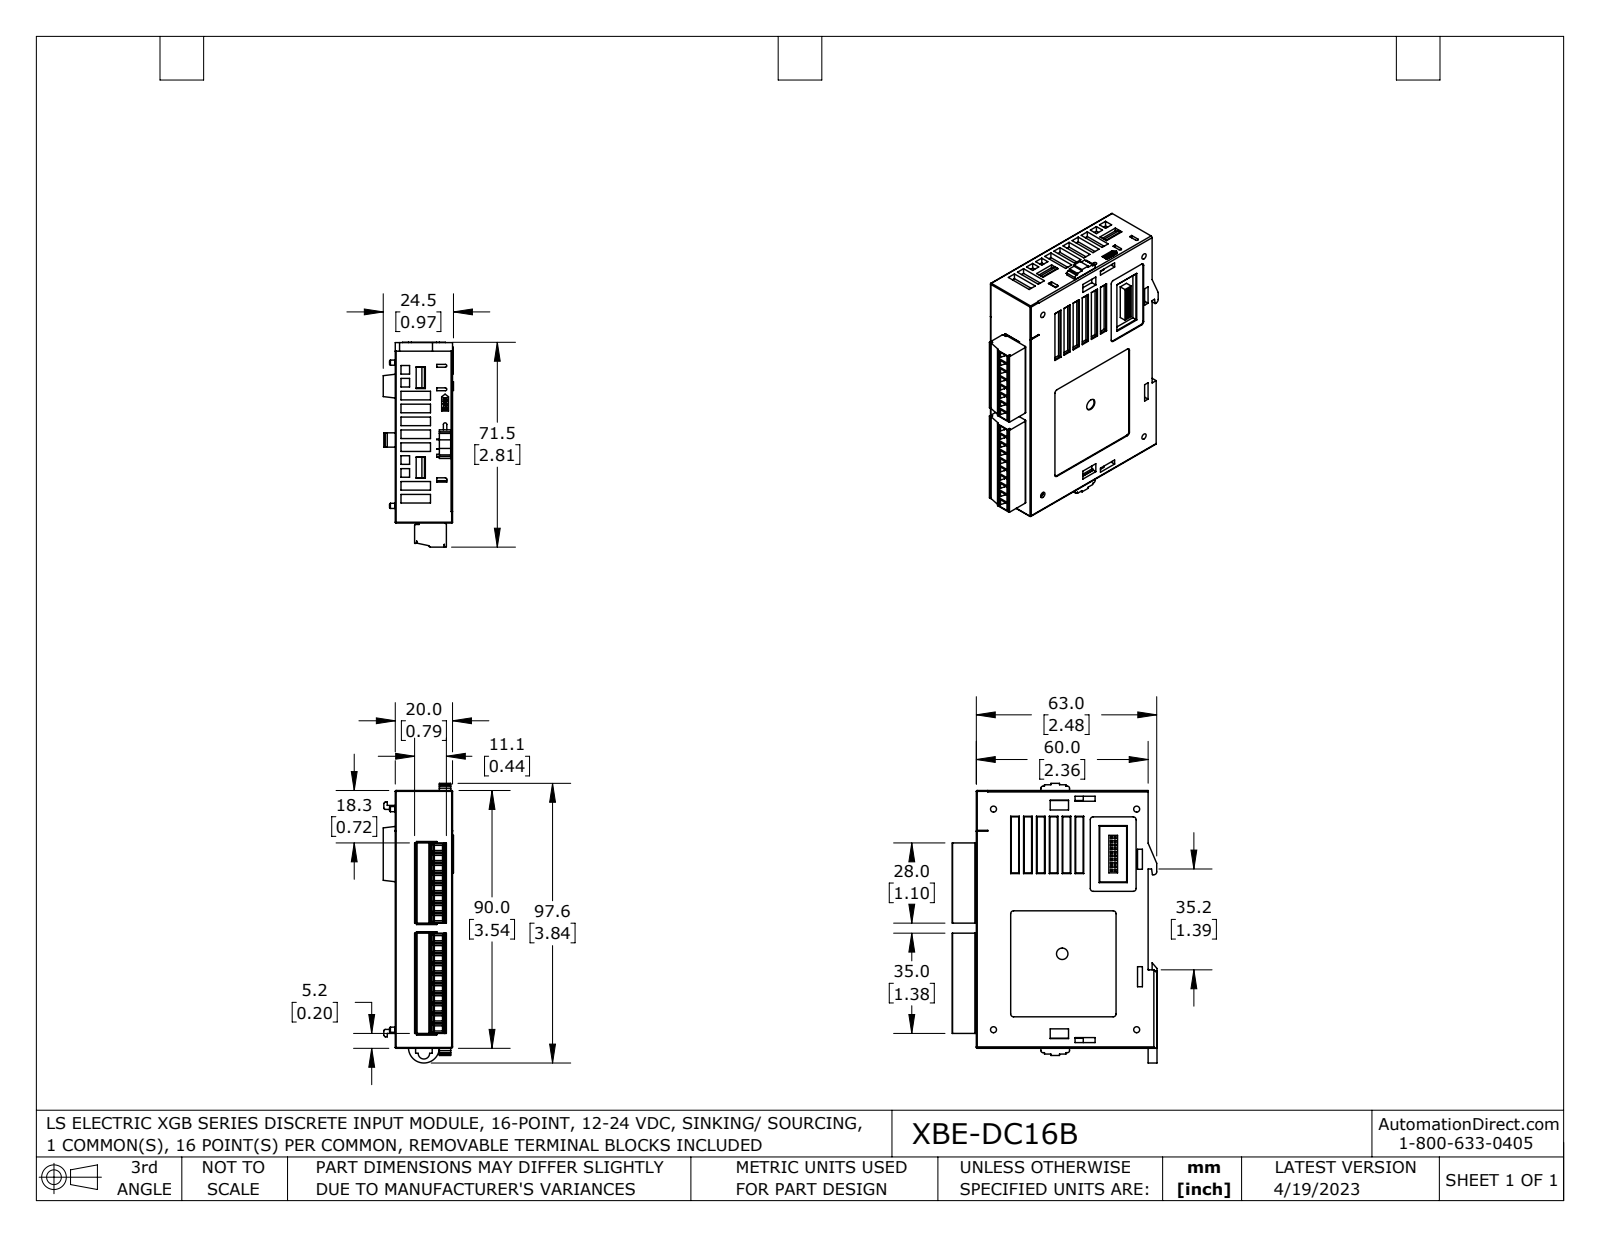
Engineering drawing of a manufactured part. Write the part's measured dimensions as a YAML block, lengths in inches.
part_name: "XBE-DC16A broken Part cut1 coord fxt"
step_written_by: "SolidWorks 2021 (AUTOMOTIVE_DESIGN)"
units: inches
bodies: {solids: 1, faces: 2854, planar: 2074, cylindrical: 541, other: 239}
overall_size: [3.844, 2.815, 0.966]
volume: 6.7
surface_area: 48.28
round_holes:
  - {diameter: 0.108, count: 18}
  - {diameter: 0.116, count: 18}
  - {diameter: 0.083, count: 4}
  - {diameter: 0.071, count: 2}
  - {diameter: 0.157, count: 1}
round_bosses_or_shafts:
  - {diameter: 0.11, count: 18}
  - {diameter: 0.071, count: 6}
partial_cylinders:
  - {radius: 0.008, count: 74}
  - {radius: 0.004, count: 72}
  - {radius: 0.012, count: 54}
  - {radius: 0.02, count: 21}
  - {radius: 0.062, count: 18}
  - {radius: 0.071, count: 18}
  - {radius: 0.039, count: 11}
  - {radius: 0.031, count: 6}
face_to_face_distances: [0.787, 0.079, 0.039, 0.776, 0.709, 0.748, 2.362, 0.669, 0.067, 0.047]
hole_center_spacings: [0.138, 0.276, 0.413, 0.551, 0.689, 0.827, 0.965, 1.102]
